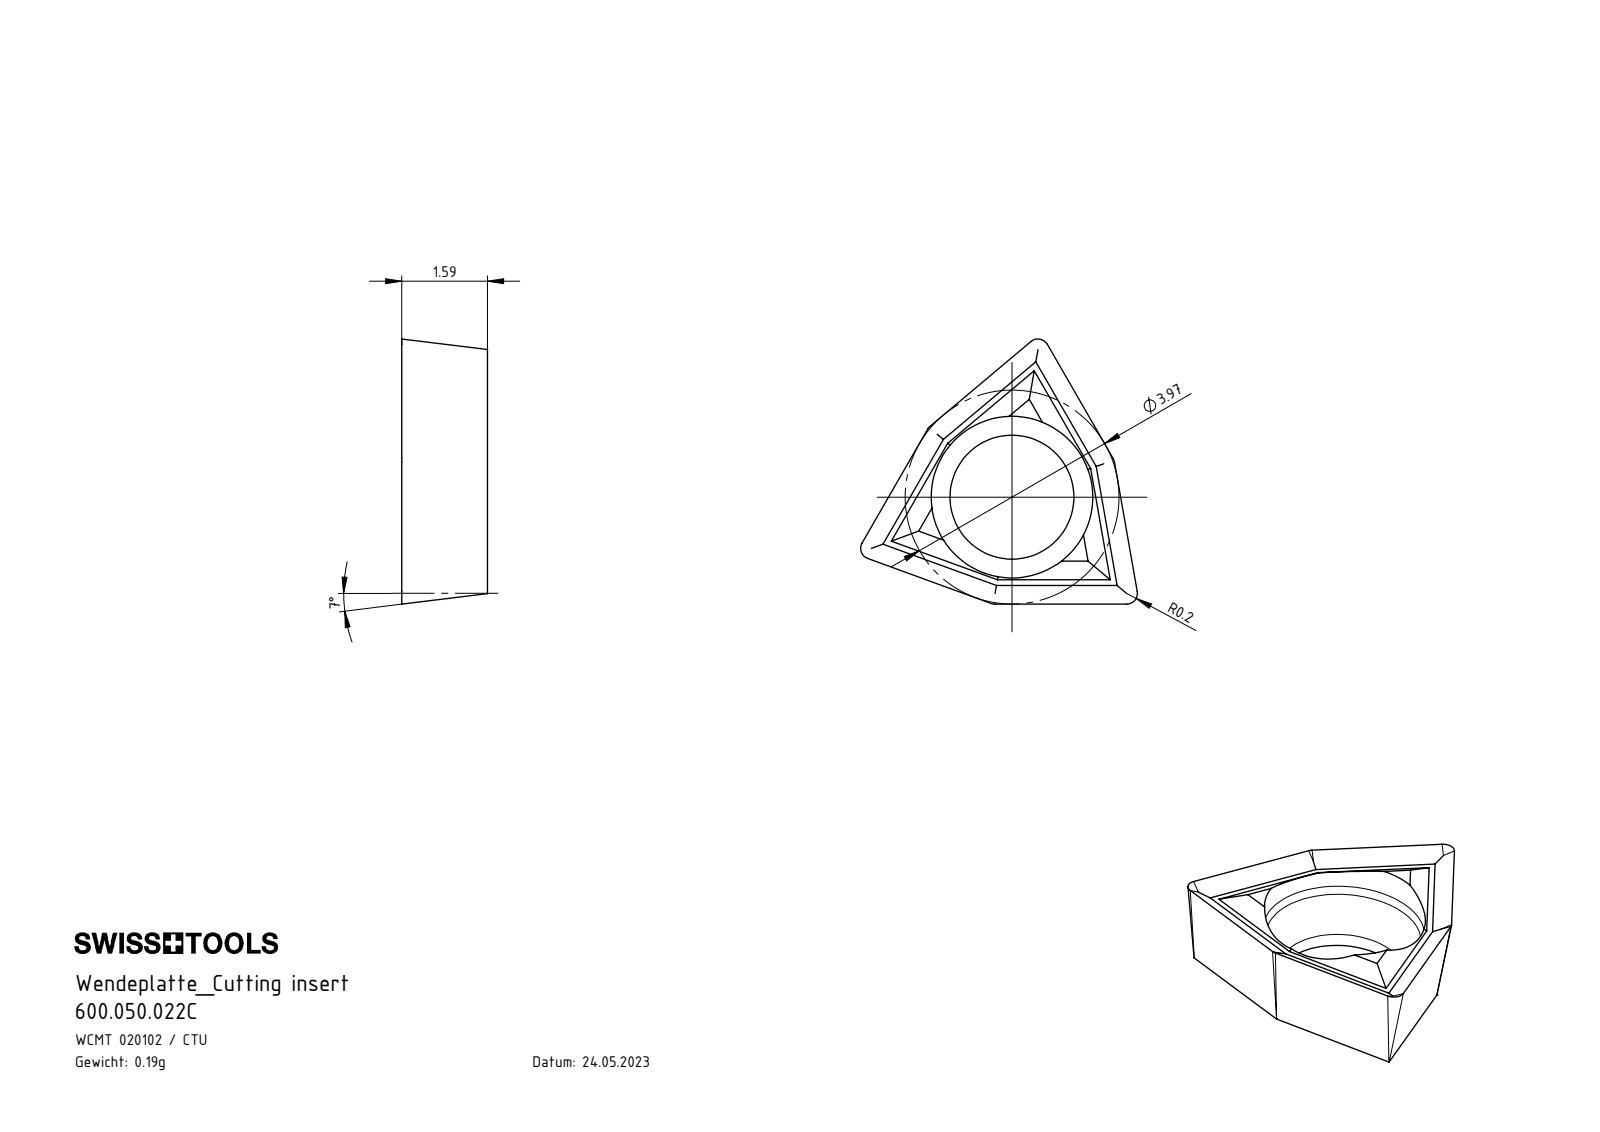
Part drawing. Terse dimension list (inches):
name: 600.050.022C
written by: SolidWorks 2022 (AUTOMOTIVE_DESIGN)
unit: in
bodies: 1 solid, 43 faces (23 planar, 4 cylindrical, 16 other)
size: 0.202 × 0.194 × 0.063
volume: 0.001 in³; area: 0.088 in²
holes: 1× ⌀0.091, 1× ⌀0.118
face distances: 0.055, 0.063
